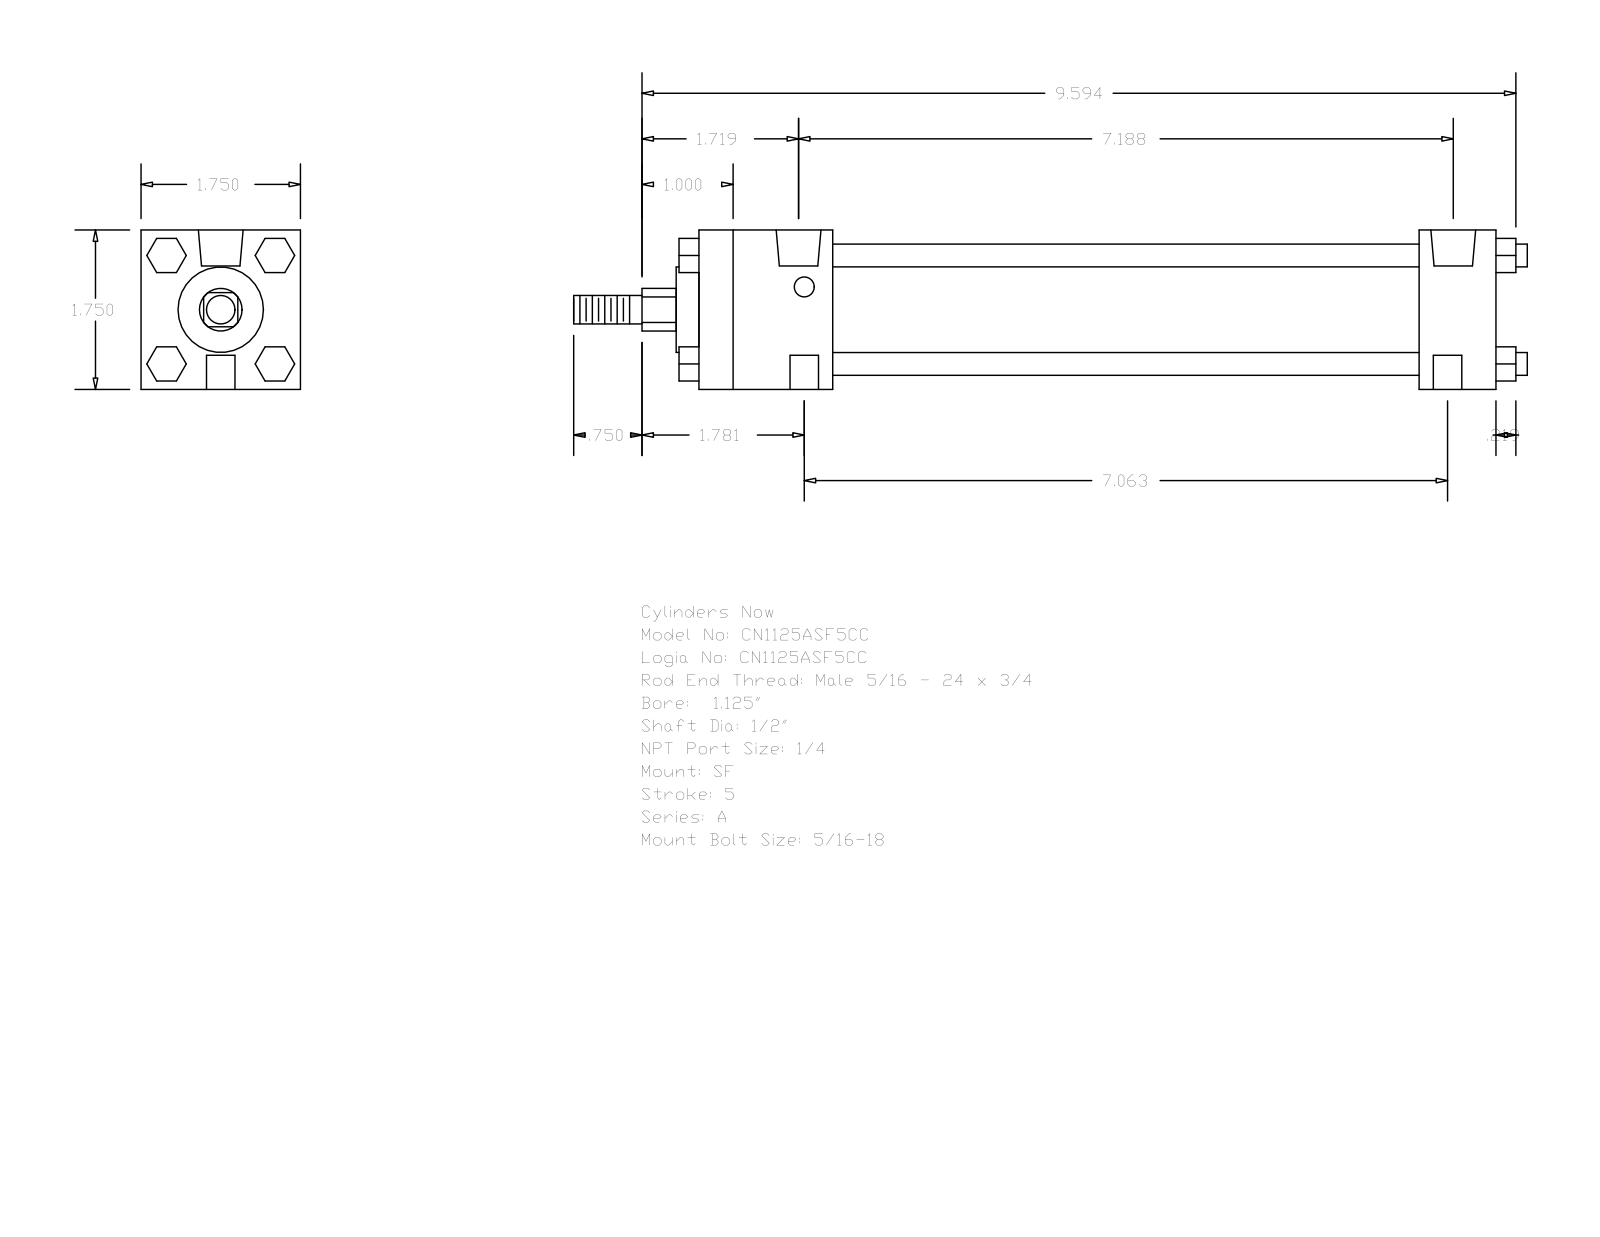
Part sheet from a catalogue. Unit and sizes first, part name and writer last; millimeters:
Units: millimetres
Overall size (bounding box): 265.91 × 44.45 × 44.45
Round holes (diameter × count): ⌀5.56 ×2, ⌀7.94 ×2, ⌀12.49 ×2
Round bosses / shafts (diameter × count): ⌀6.35 ×4, ⌀31.88 ×1, ⌀23.81 ×1, ⌀12.7 ×1, ⌀7.94 ×1
Partial cylindrical surfaces — rounded edges, fillets, slot ends (radius × count): R5.94 ×1
Main face-to-face distances: 44.46, 222.24, 200.81, 21.43, 37.3, 163.51, 184.94, 9.53, 5.59, 5.56
Hole centre spacings: 179.39, 1.58, 1.59, 180.97, 180.98, 182.56
Bodies: 0 solids, 120 faces (92 planar, 28 cylindrical, 0 other)
Part name (STEP PRODUCT): A_SF__0112_0.5
STEP written by: GSSL Pune (CONFIG_CONTROL_DESIGN)
